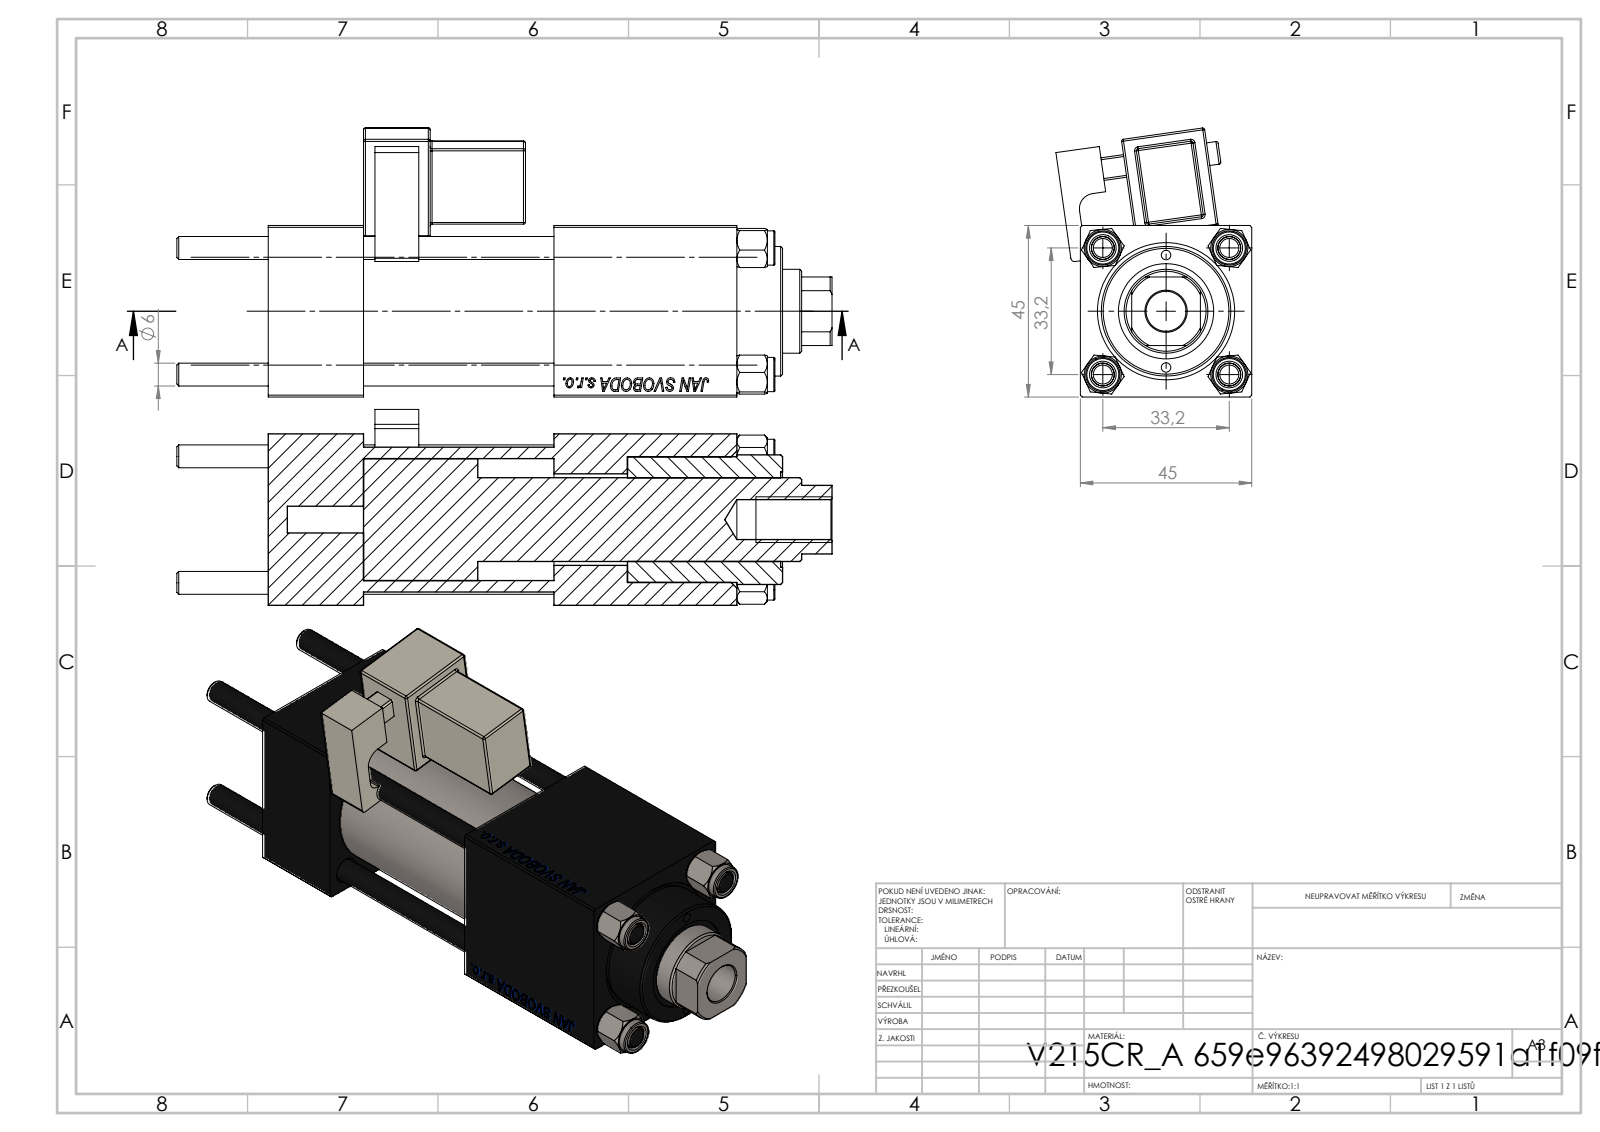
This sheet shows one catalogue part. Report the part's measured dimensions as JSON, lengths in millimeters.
{"part_name": "V215CR_VCP; CR025_012_A_0_G_A_G_M_020_+#_##_TYCINKA; NUT_M5; V215CR_BODY_A (+2 more)", "step_written_by": "SolidWorks 2019 (CONFIG_CONTROL_DESIGN)", "units": "millimeters", "bodies": {"solids": 12, "faces": 1218, "planar": 552, "cylindrical": 112, "other": 554}, "overall_size": [172, 70.58, 51.41], "volume_mm3": 234436, "surface_area_mm2": 83309, "round_holes": [[6, 4], [2.5, 2], [7, 2], [13.16, 2], [20, 2], [10.5, 1], [22, 1], [24, 1], [25, 1], [32, 1], [33, 1]], "round_bosses_or_shafts": [[9, 4], [38, 1], [34, 1], [6, 1]], "partial_cylinders_radius": [[0.5, 24], [1, 1], [2.5, 1], [4, 1], [10.5, 1]], "face_to_face_distances": [45, 25, 123, 50, 75, 98, 48, 94.3, 69.3, 19.3], "hole_center_spacings": [16.7, 23.48, 33.2, 35.47, 14.75, 46.95, 29.5, 75.5]}
